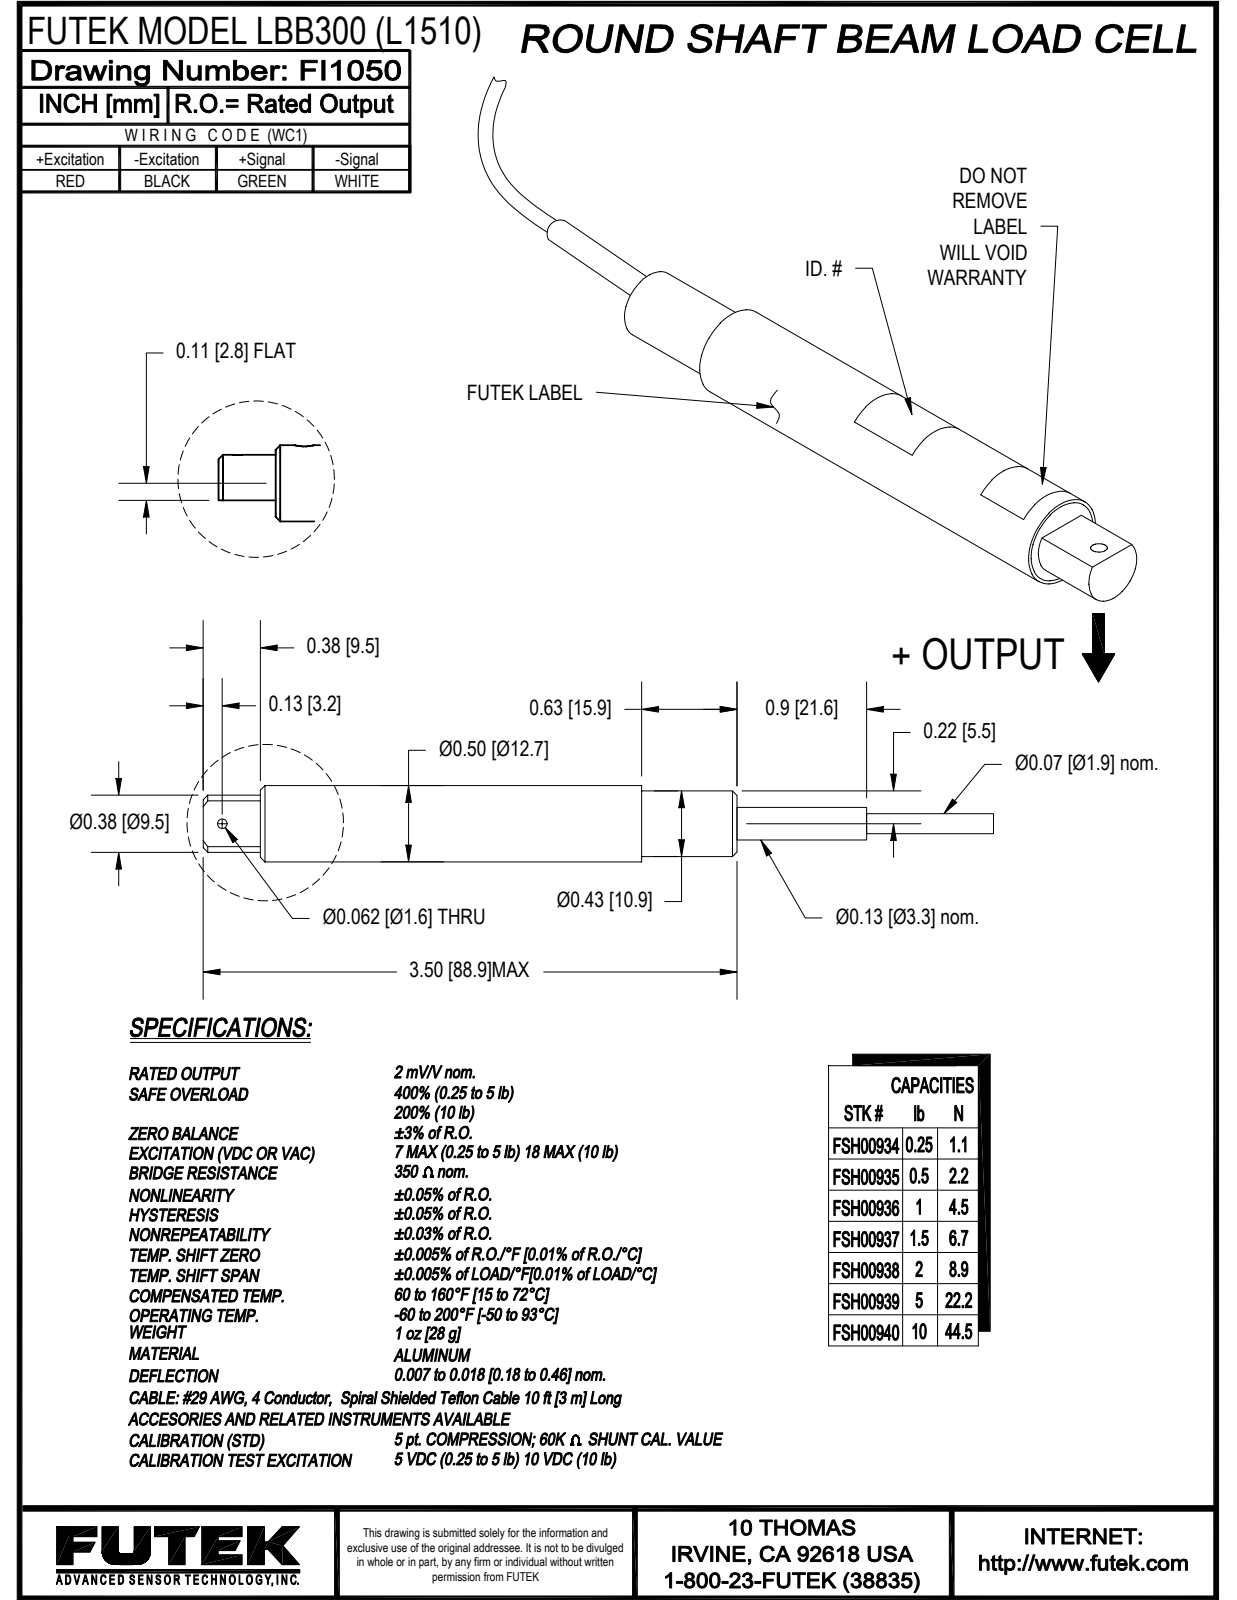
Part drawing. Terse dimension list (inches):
name: LBB300; 1EEF; 1EEFA
written by: Autodesk Inventor 2008 (AUTOMOTIVE_DESIGN)
unit: in
bodies: 2 solids, 116 faces (21 planar, 15 cylindrical, 80 other)
size: 5.986 × 0.56 × 0.5
volume: 0.54 in³; area: 13.9 in²
holes: 2× ⌀0.125, 1× ⌀0.062, 1× ⌀0.077, 1× ⌀0.089, 1× ⌀0.437, 1× ⌀0.45
bosses: 3× ⌀0.081, 1× ⌀0.5, 1× ⌀0.449, 1× ⌀0.43, 1× ⌀0.375, 1× ⌀0.112
face distances: 3.5, 2.25, 1.25, 0.375, 1.875, 3.125, 2.875, 2.5, 0.625, 0.625
hole spacings: 0.115, 0.437
